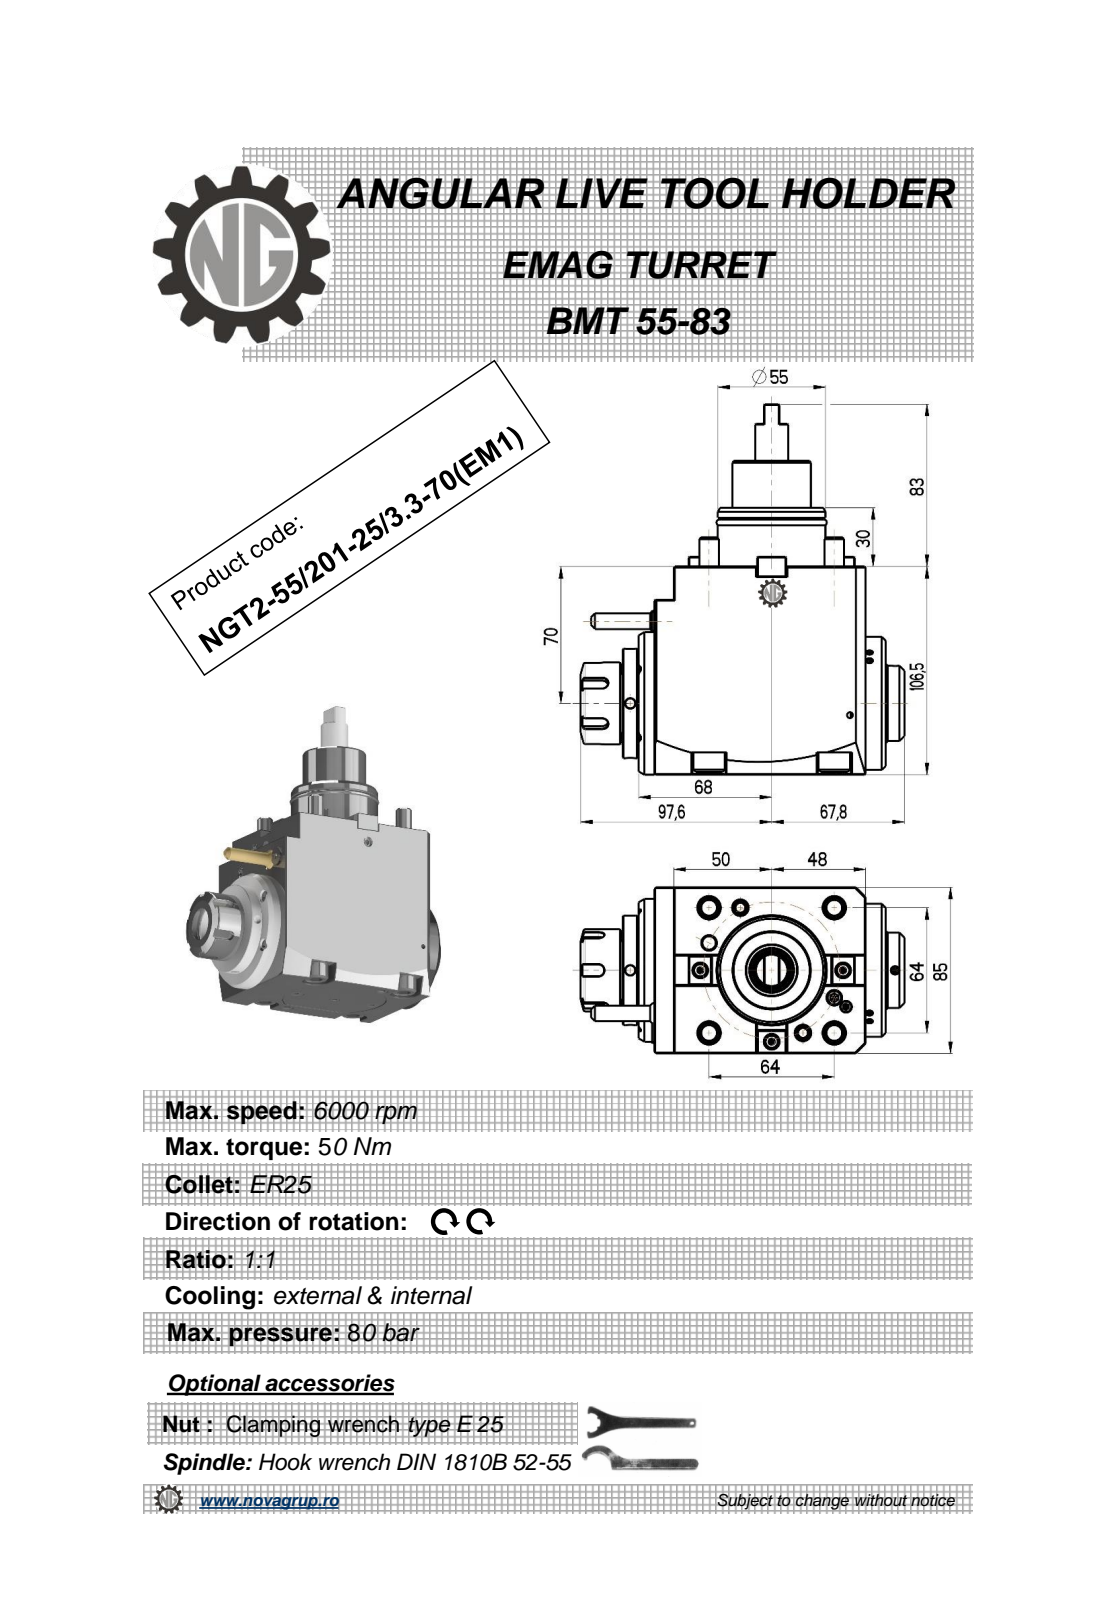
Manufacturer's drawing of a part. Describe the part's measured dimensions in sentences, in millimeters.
The part is named "NGT2_55_201_25_3_3_70_EM1". Its 3-D file was written by "PRO/ENGINEER BY PARAMETRIC TECHNOLOGY CORPORATION, 2010280 (CONFIG_CONTROL_DESIGN)". It is 2 solids with 489 faces: 229 planar, 111 cylindrical and 149 other. Overall it measures 189.5 by 165.4 by 85 millimeters. Its volume is 1 179 000 cubic millimeters and its surface area 104 063 square millimeters. Round holes: 3 of diameter 5, 2 of diameter 6.8, 1 of diameter 3, 1 of diameter 12. Round bosses or shafts: 4 of diameter 16, 4 of diameter 10, 1 of diameter 73, 1 of diameter 68, 1 of diameter 56, 1 of diameter 55, 1 of diameter 50, 1 of diameter 43.4. Partial cylindrical surfaces (rounded edges, fillets, slot ends): 20 of radius 0.32, 6 of radius 0.22, 5 of radius 3, 4 of radius 8.5, 2 of radius 0.8, 2 of radius 480. The main face-to-face distances are 85, 106.5, 8, 108, 116, 16, 10, 126.3, 118.3, 10.3. The hole center spacings are 42.62, 69.86, 105.19.
